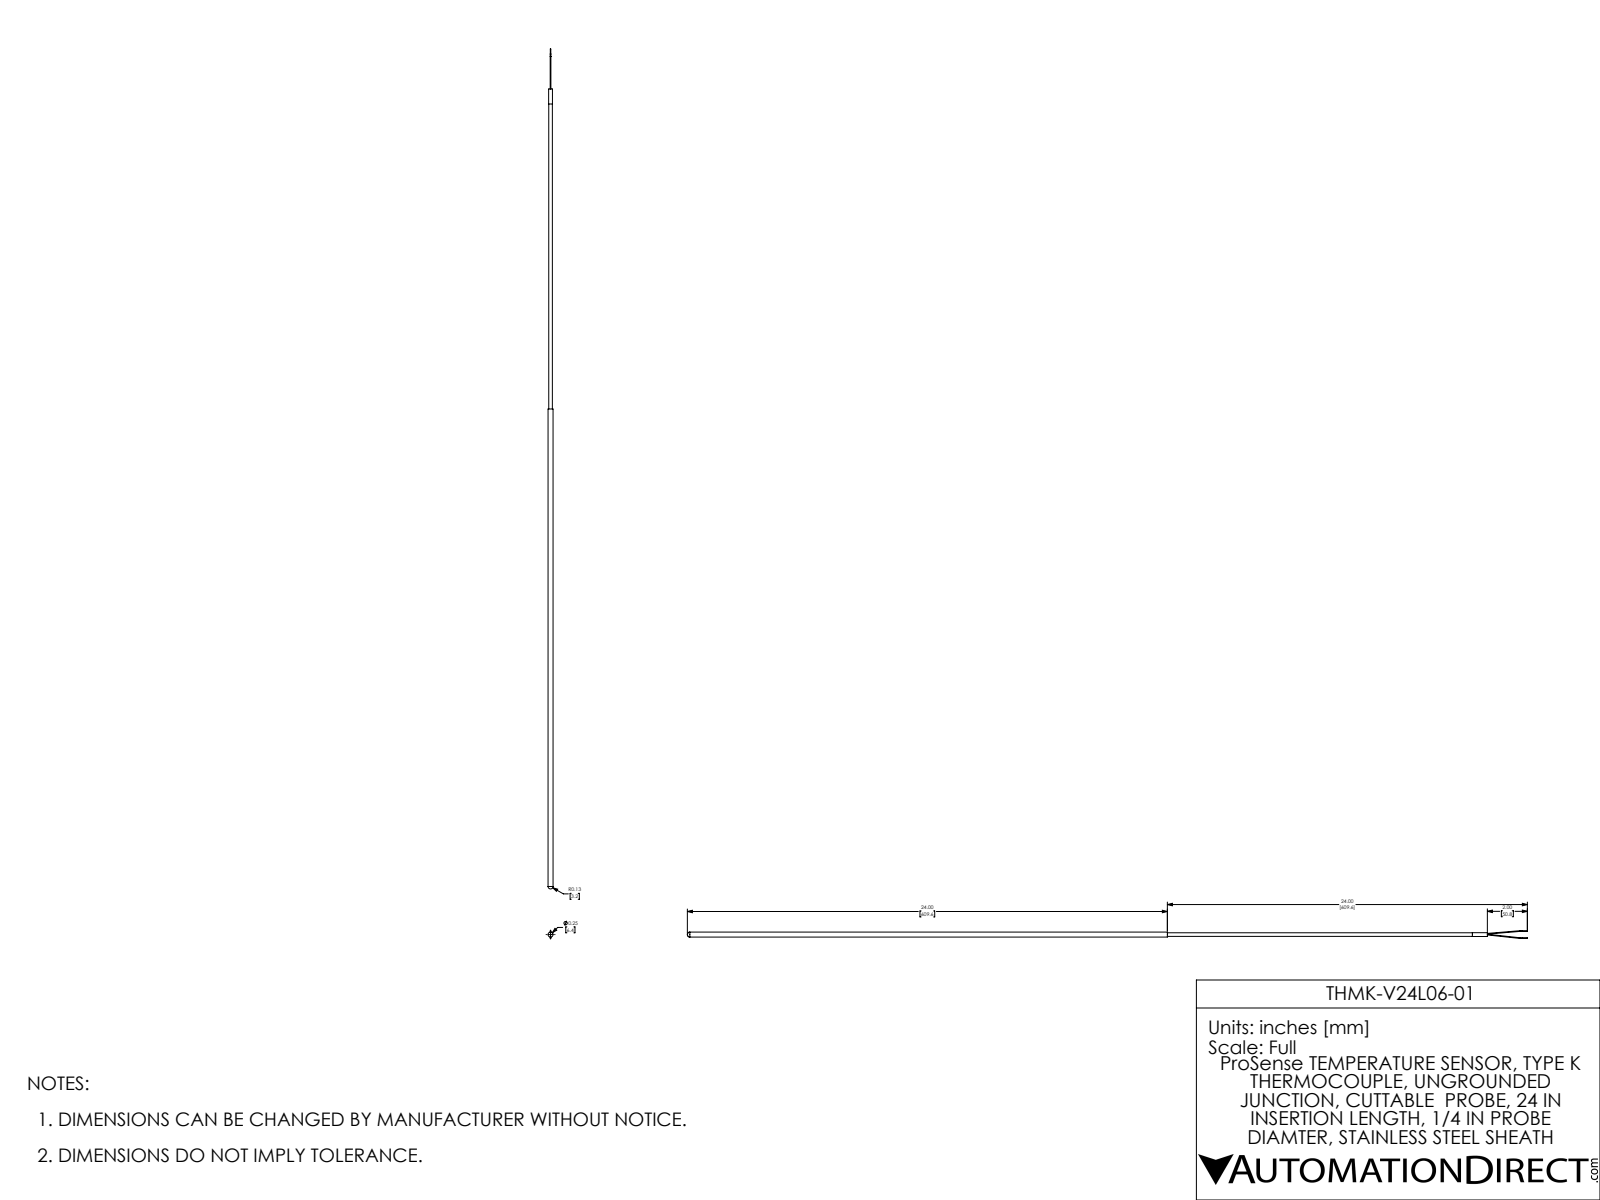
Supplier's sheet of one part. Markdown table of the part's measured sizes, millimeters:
| quantity | value |
| --- | --- |
| part name | THMK-V24L06-01 |
| STEP written by | SolidWorks 2017 (AUTOMOTIVE_DESIGN) |
| units | millimeters |
| bodies | 4 solids, 33 faces (10 planar, 18 cylindrical, 5 other) |
| overall size | 1066.7 × 9.8 × 6.4 |
| volume | 26 100 mm³ |
| surface area | 18 650 mm² |
| round bosses / shafts (diameter × count) | 0.9 × 4, 0.6 × 2, 6.4 × 1, 4.8 × 1, 4.6 × 1 |
| main face-to-face distances | 406.4, 50.8, 19.1, 387.4, 31.8, 355.6, 69.9, 101.6, 457.2, 6.4 |
